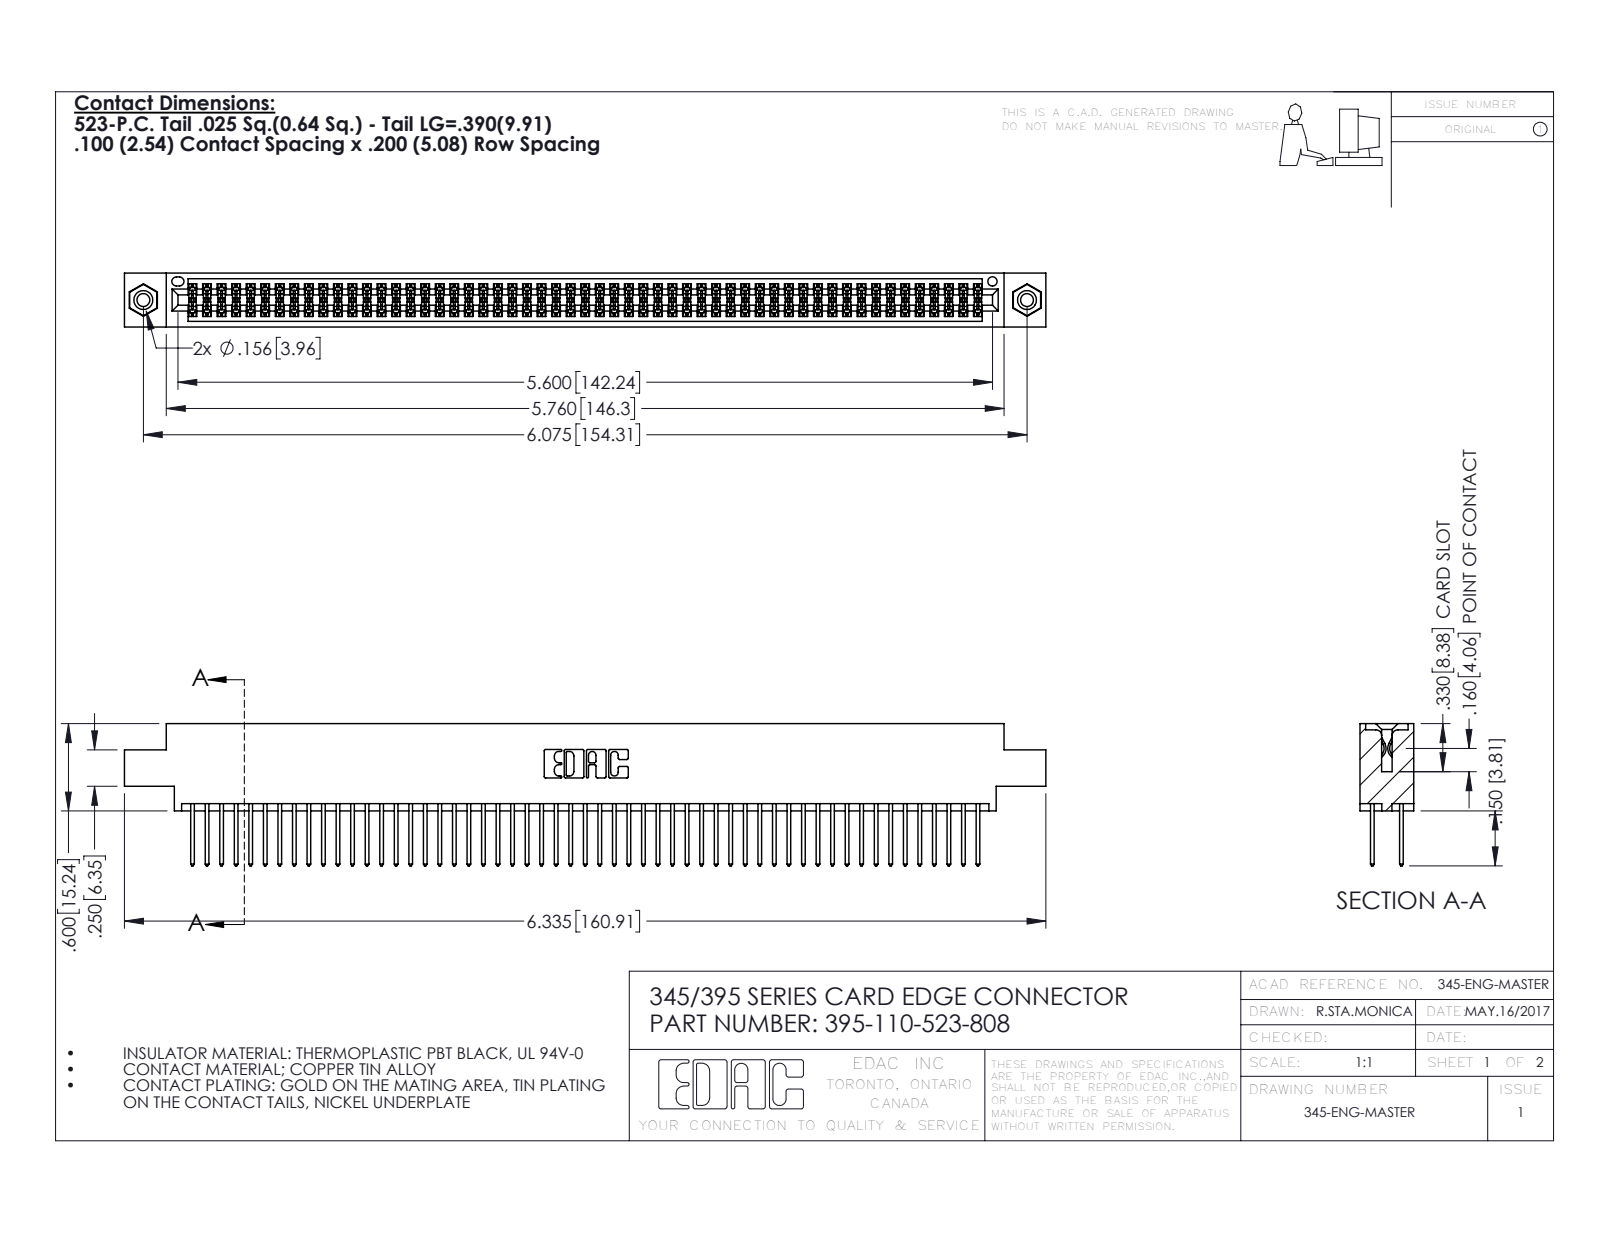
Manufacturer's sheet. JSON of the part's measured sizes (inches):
{"part_name": "345-250-001_345-250-003-102; 395-110-523-808; 345 Part_0.170 Offset - 0.156 Dia-TI; 345-292-001_345-293-123", "step_written_by": "SolidWorks 2016 (CONFIG_CONTROL_DESIGN)", "units": "inches", "bodies": {"solids": 113, "faces": 5690, "planar": 3746, "cylindrical": 1928, "other": 16}, "overall_size": [6.335, 0.977, 0.37], "volume_in3": 0.968, "surface_area_in2": 38.53, "round_holes": [[0.089, 2], [0.125, 2], [0.156, 2], [0.064, 1]], "round_bosses_or_shafts": [[0.155, 2]], "partial_cylinders_radius": [[0.006, 165], [0.01, 110], [0.01, 22], [0.007, 6], [0.031, 6], [0.026, 3], [0.014, 2], [0.019, 2]], "face_to_face_distances": [0.072, 0.298, 0.2, 0.098, 0.272, 0.025, 0.37, 0.225, 0.175, 0.149], "hole_center_spacings": [0.27, 5.839, 6.075]}
